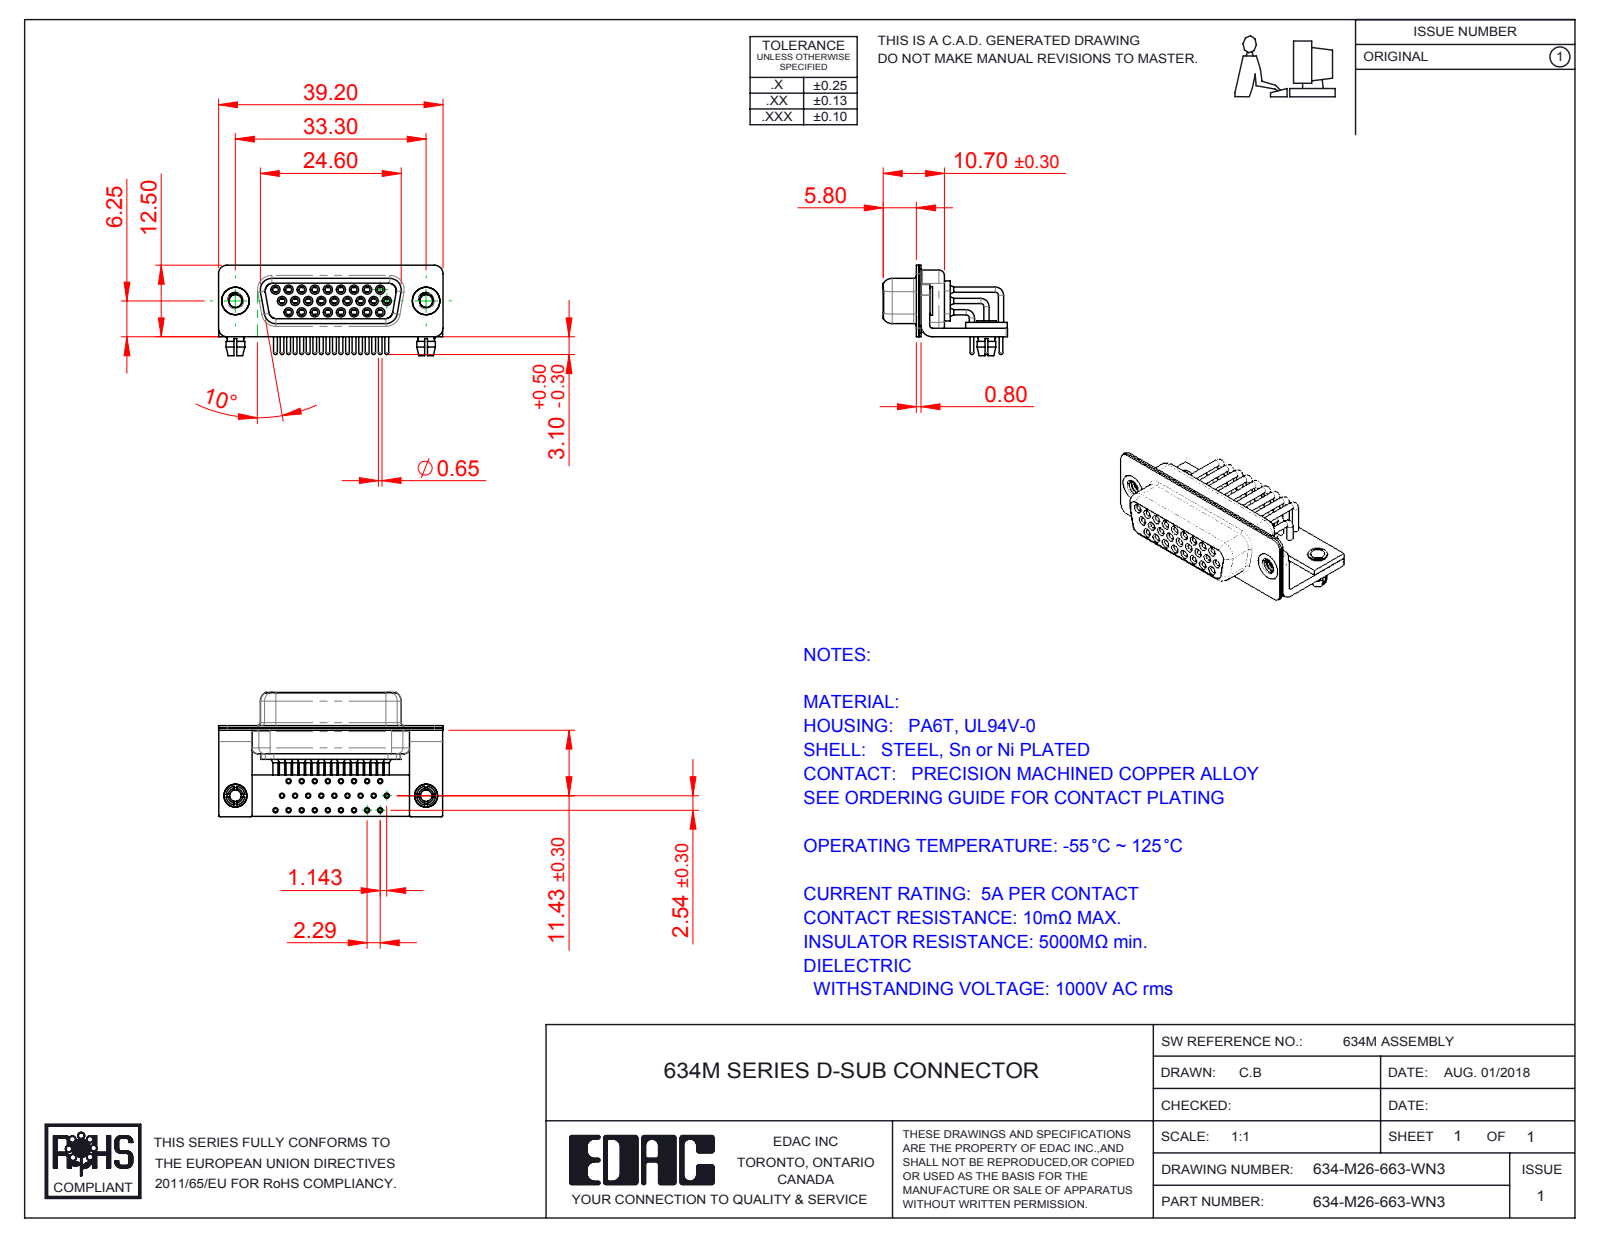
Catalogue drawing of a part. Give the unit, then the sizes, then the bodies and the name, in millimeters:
Units: millimetres
Overall size (bounding box): 39.2 × 21.7 × 15.8
Round holes (diameter × count): ⌀2 ×28, ⌀0.9 ×26, ⌀1 ×26, ⌀1.1 ×26, ⌀1.7 ×26, ⌀1.8 ×26, ⌀2.26 ×2, ⌀2.5 ×2, ⌀3.2 ×2, ⌀4 ×2, ⌀4.8 ×2
Round bosses / shafts (diameter × count): ⌀0.9 ×27, ⌀1.6 ×26, ⌀1.5 ×26, ⌀0.65 ×26, ⌀5 ×2, ⌀4.9 ×2, ⌀4 ×2, ⌀3.4 ×2
Partial cylindrical surfaces — rounded edges, fillets, slot ends (radius × count): R0.25 ×16, R1.5 ×16, R2 ×13, R1.35 ×8, R1.6 ×8, R0.5 ×5, R0.6 ×4, R0.65 ×4
Main face-to-face distances: 0.4, 2.3, 0.8, 1, 1.5, 1.9, 9.35, 1.45, 8.95, 0.85
Hole centre spacings: 4.57, 2.29, 2.28, 3.96, 6.05, 6.86, 4.27, 2.78
Volume: 3 109 mm³ · Surface area: 10 013 mm²
Bodies: 36 solids, 1851 faces (531 planar, 841 cylindrical, 479 other)
Part name (STEP PRODUCT): 634M Contact Row 1; 634-M26-663-WN3; 634M Contact Row 2; 634M Board Lock (+7 more)
STEP written by: SolidWorks 2016 (CONFIG_CONTROL_DESIGN)
